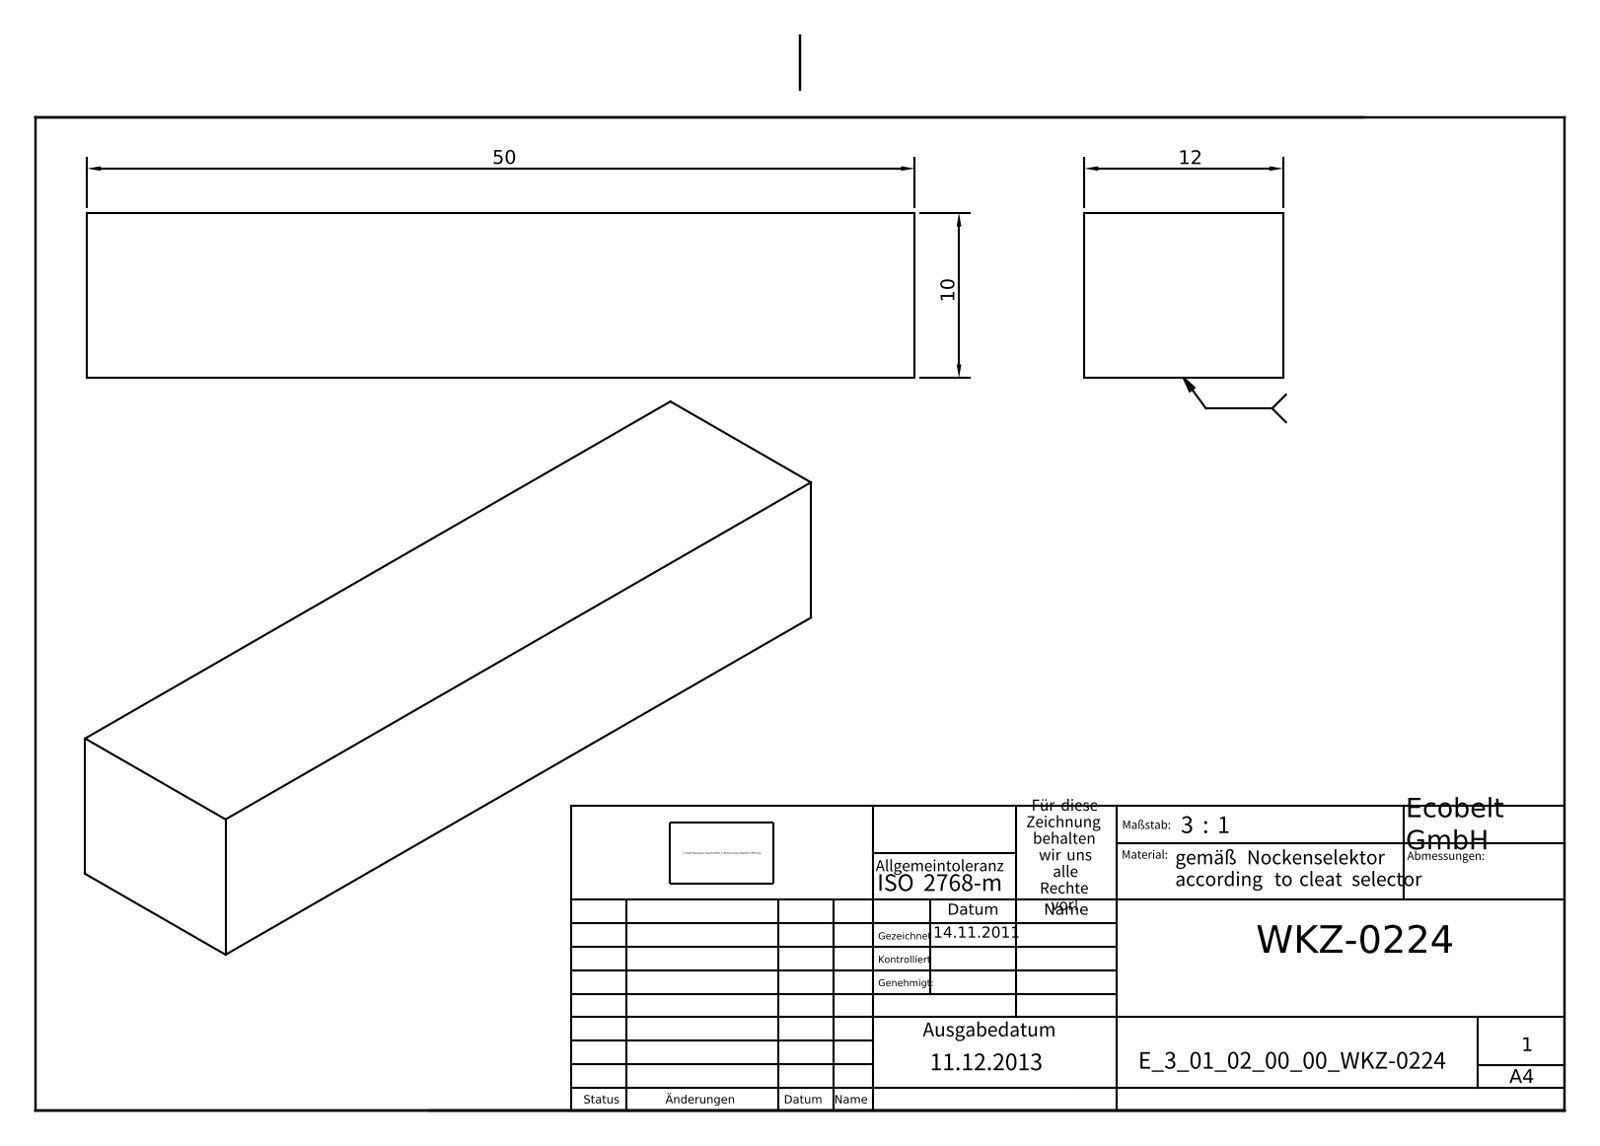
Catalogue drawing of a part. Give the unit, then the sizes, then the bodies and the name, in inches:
Units: inches
Overall size (bounding box): 1.969 × 0.472 × 0.394
Main face-to-face distances: 0.394, 0.472, 1.969
Volume: 0.366 in³ · Surface area: 3.782 in²
Bodies: 1 solid, 6 faces (6 planar, 0 cylindrical, 0 other)
Part name (STEP PRODUCT): E_3_01_02_00_00_WKZ-0224
STEP written by: Autodesk Inventor 2021 (AUTOMOTIVE_DESIGN)
